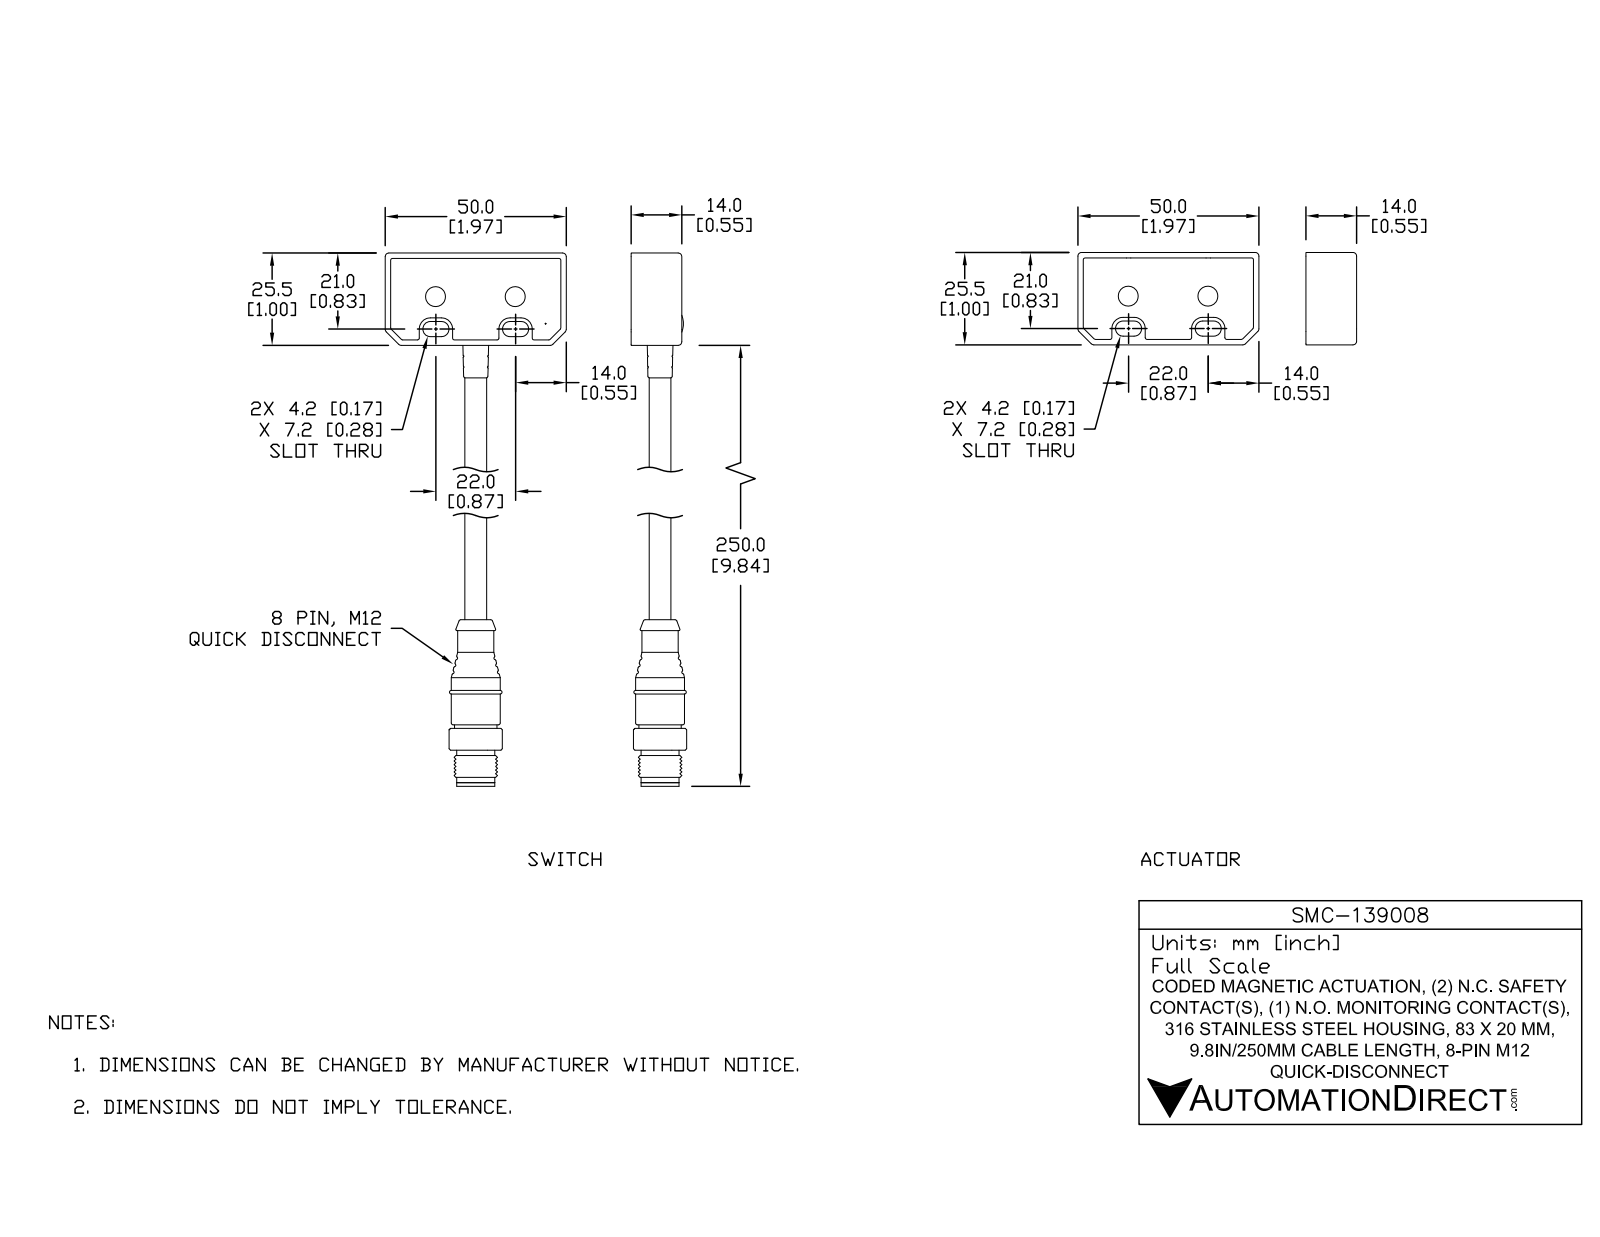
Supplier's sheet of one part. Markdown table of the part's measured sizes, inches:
| quantity | value |
| --- | --- |
| part name | SMC-139008_1; SMC-139008_2; SMC-139008 |
| STEP written by | SolidWorks 2017 (AUTOMOTIVE_DESIGN) |
| units | inches |
| bodies | 13 solids, 1243 faces (411 planar, 485 cylindrical, 347 other) |
| overall size | 11.89 × 1.969 × 0.604 |
| volume | 1.542 in³ |
| surface area | 43.67 in² |
| round holes (diameter × count) | 0.197 × 4, 0.119 × 1, 0.177 × 1, 0.213 × 1, 0.232 × 1, 0.287 × 1, 0.327 × 1, 0.465 × 1 |
| round bosses / shafts (diameter × count) | 0.031 × 10, 0.193 × 4, 0.079 × 4, 0.531 × 1, 0.461 × 1, 0.413 × 1, 0.394 × 1, 0.374 × 1 |
| partial cylindrical surfaces (radius × count) | 0.02 × 80, 0.012 × 74, 0.039 × 40, 0.083 × 8, 0.122 × 8, 0.128 × 8, 0.142 × 8, 0.175 × 8 |
| main face-to-face distances | 0.059, 0.543, 0.055, 0.488, 0.484, 0.429, 0.098, 0.945, 1.043, 1.909 |
| hole center spacings | 0.866, 0.988, 0.472, 1.27, 1.309, 1.319, 1.332, 1.775 |
